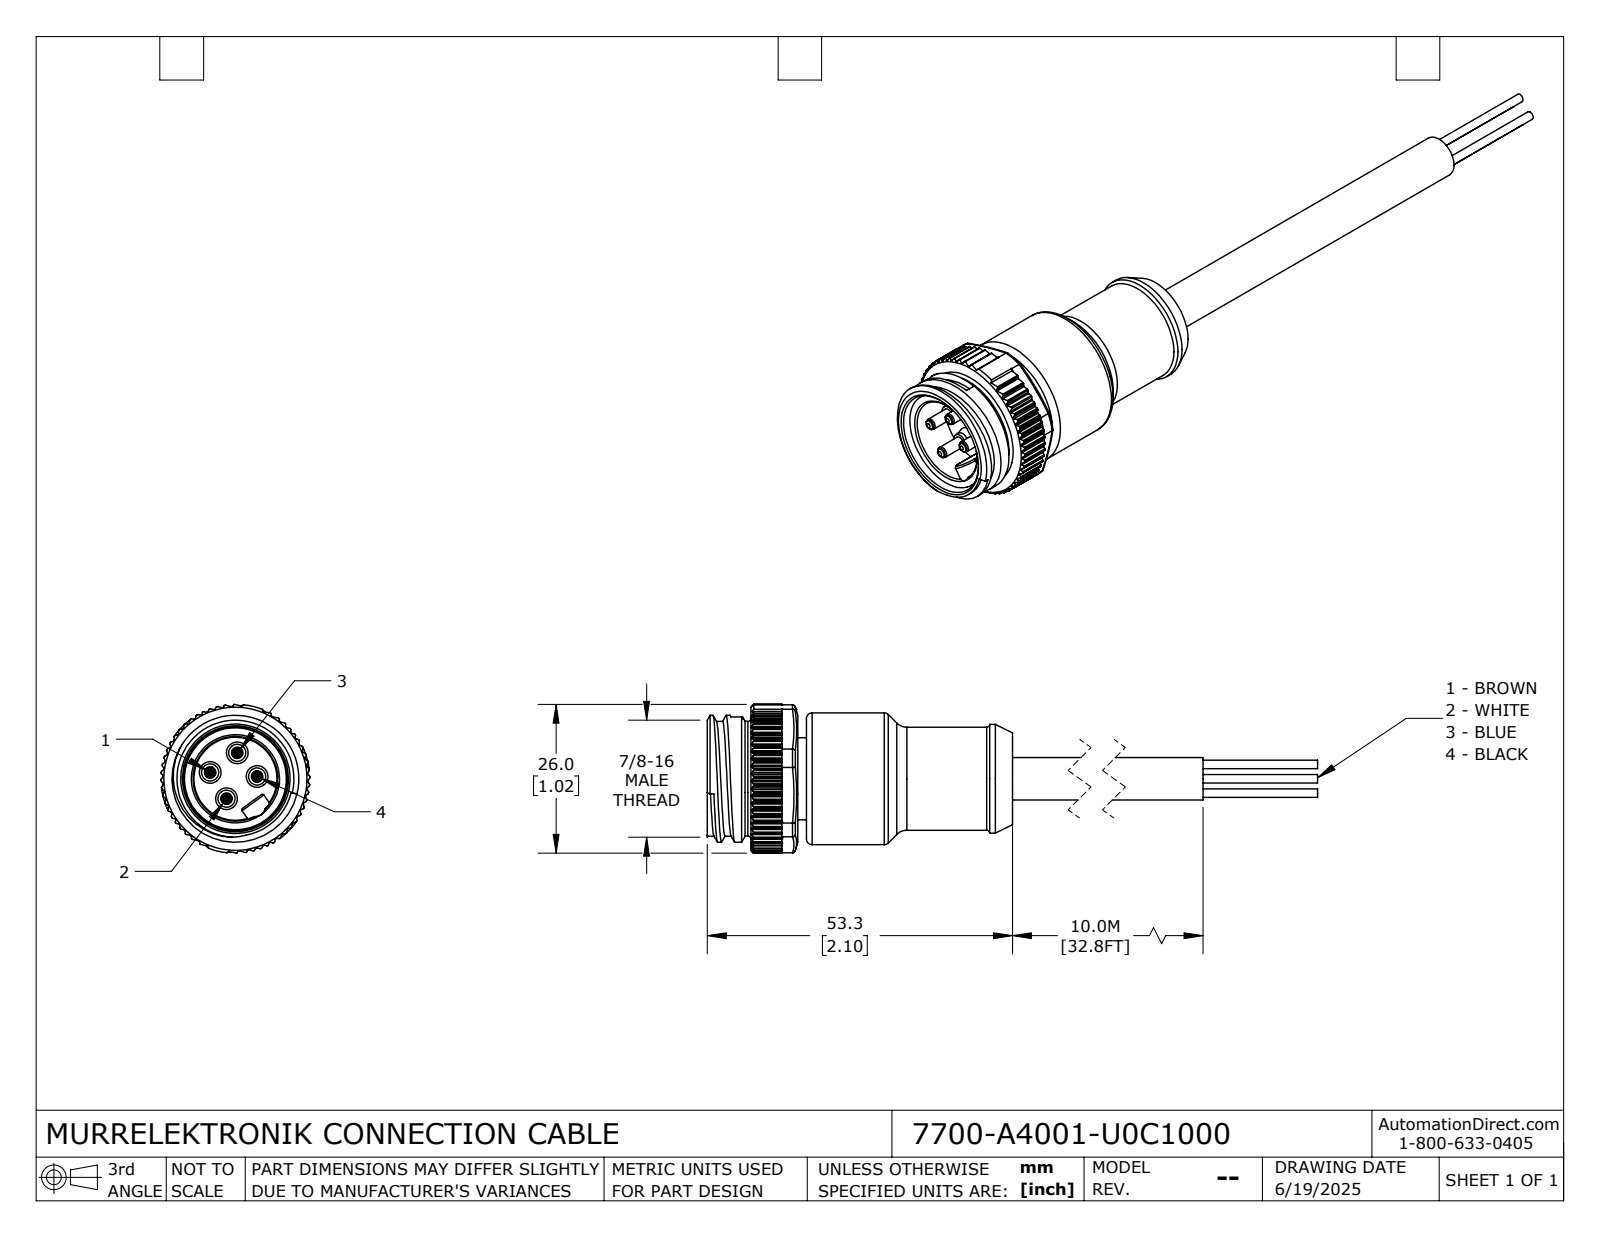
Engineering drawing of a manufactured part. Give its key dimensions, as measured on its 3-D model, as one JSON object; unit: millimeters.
{"part_name": "7700-A4001-U0C1000", "step_written_by": "SolidWorks 2024 (CONFIG_CONTROL_DESIGN)", "units": "millimeters", "bodies": {"solids": 1, "faces": 580, "planar": 236, "cylindrical": 266, "other": 78}, "overall_size": [143.3, 26, 26], "volume_mm3": 20106, "surface_area_mm2": 9287, "round_holes": [[15.6, 1], [18.5, 1]], "round_bosses_or_shafts": [[3, 4], [2, 4], [1.5, 4], [23, 1], [22.17, 1], [20.05, 1], [20, 1], [19, 1]], "partial_cylinders_radius": [[0.2, 126], [0.3, 18], [0.1, 4], [0.7, 4], [2.35, 1], [13, 1]], "face_to_face_distances": [1.5, 37.5, 36, 8.2, 9.7, 45.7, 0.9, 7.3, 8.8, 44.8]}
